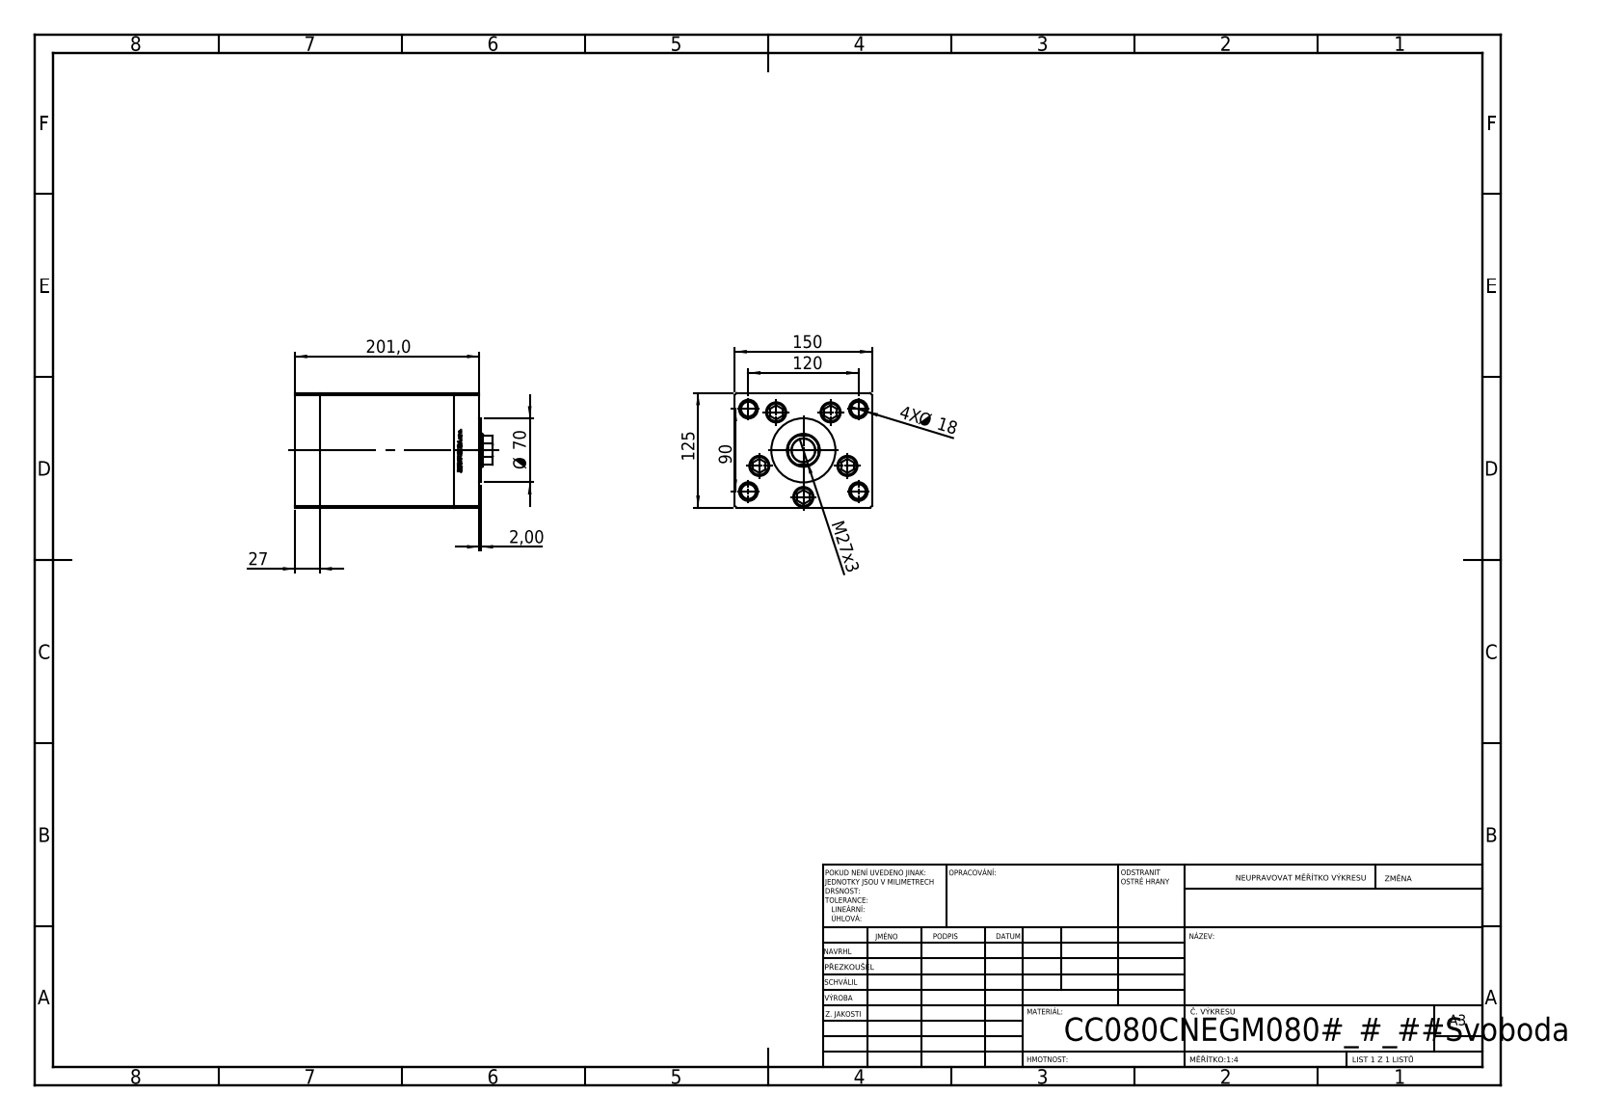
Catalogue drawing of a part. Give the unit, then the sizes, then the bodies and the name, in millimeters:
Units: millimetres
Overall size (bounding box): 216 × 150 × 125
Round holes (diameter × count): ⌀17.5 ×9, ⌀22 ×5, ⌀16 ×4, ⌀20.5 ×4, ⌀21 ×1, ⌀25.5 ×1, ⌀36 ×1
Round bosses / shafts (diameter × count): ⌀8 ×5, ⌀21 ×4, ⌀80 ×1, ⌀70 ×1
Partial cylindrical surfaces — rounded edges, fillets, slot ends (radius × count): R0.93 ×2, R17.5 ×1
Main face-to-face distances: 27, 174, 147, 125, 150, 33.5, 201, 6.5, 167.5, 140.5
Hole centre spacings: 51, 75, 30.43, 30.48, 58.89, 60.3, 61.25, 63.14
Volume: 3 126 000 mm³ · Surface area: 378 820 mm²
Bodies: 13 solids, 1159 faces (538 planar, 159 cylindrical, 462 other)
Part name (STEP PRODUCT): V220C BACK_C; ALLEN BOLT; V220C_C MIDDLE; V220C FRONT (+1 more)
STEP written by: SolidWorks 2019 (CONFIG_CONTROL_DESIGN)
